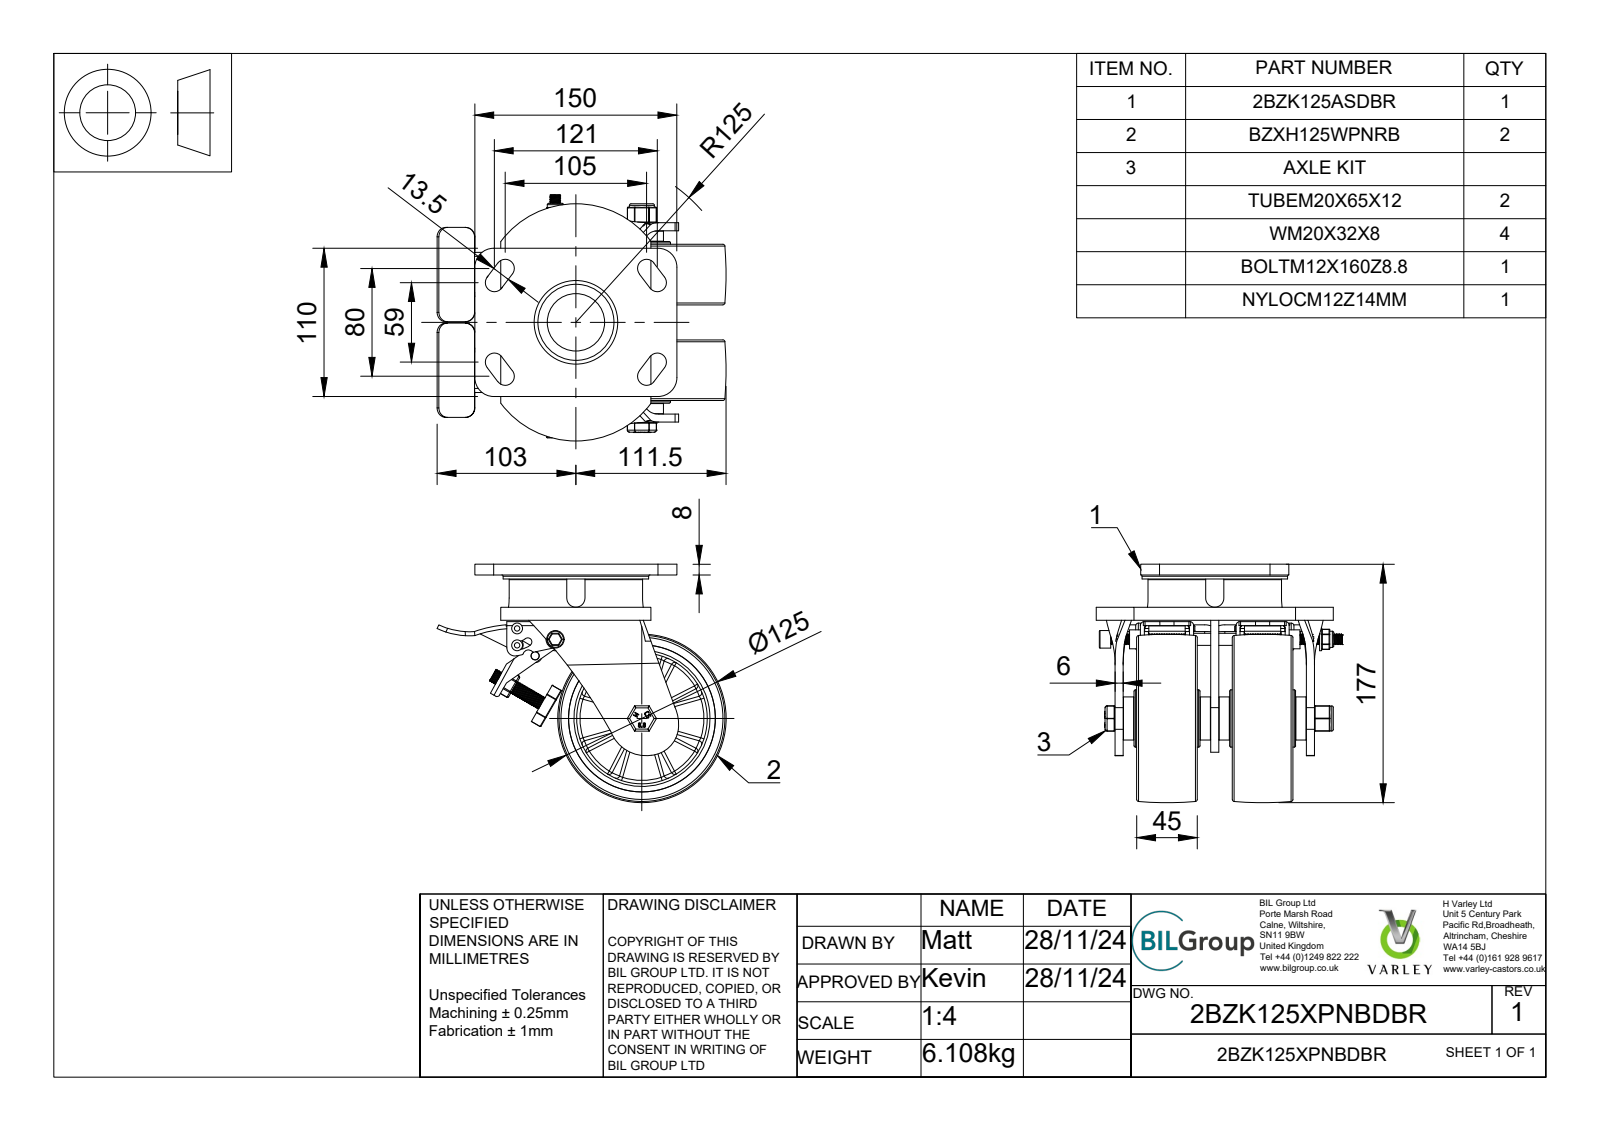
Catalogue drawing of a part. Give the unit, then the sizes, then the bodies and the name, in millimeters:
Units: millimetres
Overall size (bounding box): 214.5 × 182.75 × 177
Round holes (diameter × count): ⌀6 ×2, ⌀10 ×2, ⌀4 ×1, ⌀8 ×1, ⌀12 ×1, ⌀12.3 ×1, ⌀13 ×1, ⌀14 ×1, ⌀20 ×1, ⌀20.5 ×1, ⌀21 ×1, ⌀30 ×1
Round bosses / shafts (diameter × count): ⌀5 ×10, ⌀12 ×3, ⌀9.85 ×2, ⌀8 ×2, ⌀108 ×1, ⌀100 ×1, ⌀42.5 ×1, ⌀32 ×1
Partial cylindrical surfaces — rounded edges, fillets, slot ends (radius × count): R0.5 ×54, R1 ×24, R1.5 ×14, R0.25 ×12, R6.75 ×10, R3 ×9, R7 ×8, R0.47 ×4
Main face-to-face distances: 71, 8, 10, 16, 61, 55, 33.6, 6, 24, 41.6
Hole centre spacings: 12.5, 15.51, 19.35, 24.3, 28.78, 29.54, 71, 87.06
Volume: 1 316 000 mm³ · Surface area: 458 424 mm²
Bodies: 62 solids, 1881 faces (539 planar, 842 cylindrical, 500 other)
Part name (STEP PRODUCT): 2BZK125XPNBDBR v4; BZXH125WPNRB v1; POLYURETHANE TYRE; NYLON RIM (+7 more)
STEP written by: Autodesk Translation Framework v13.20.0.188 (AP242_MANAGED_MODEL_BASED_3D_ENGINEERING_MIM_LF)
